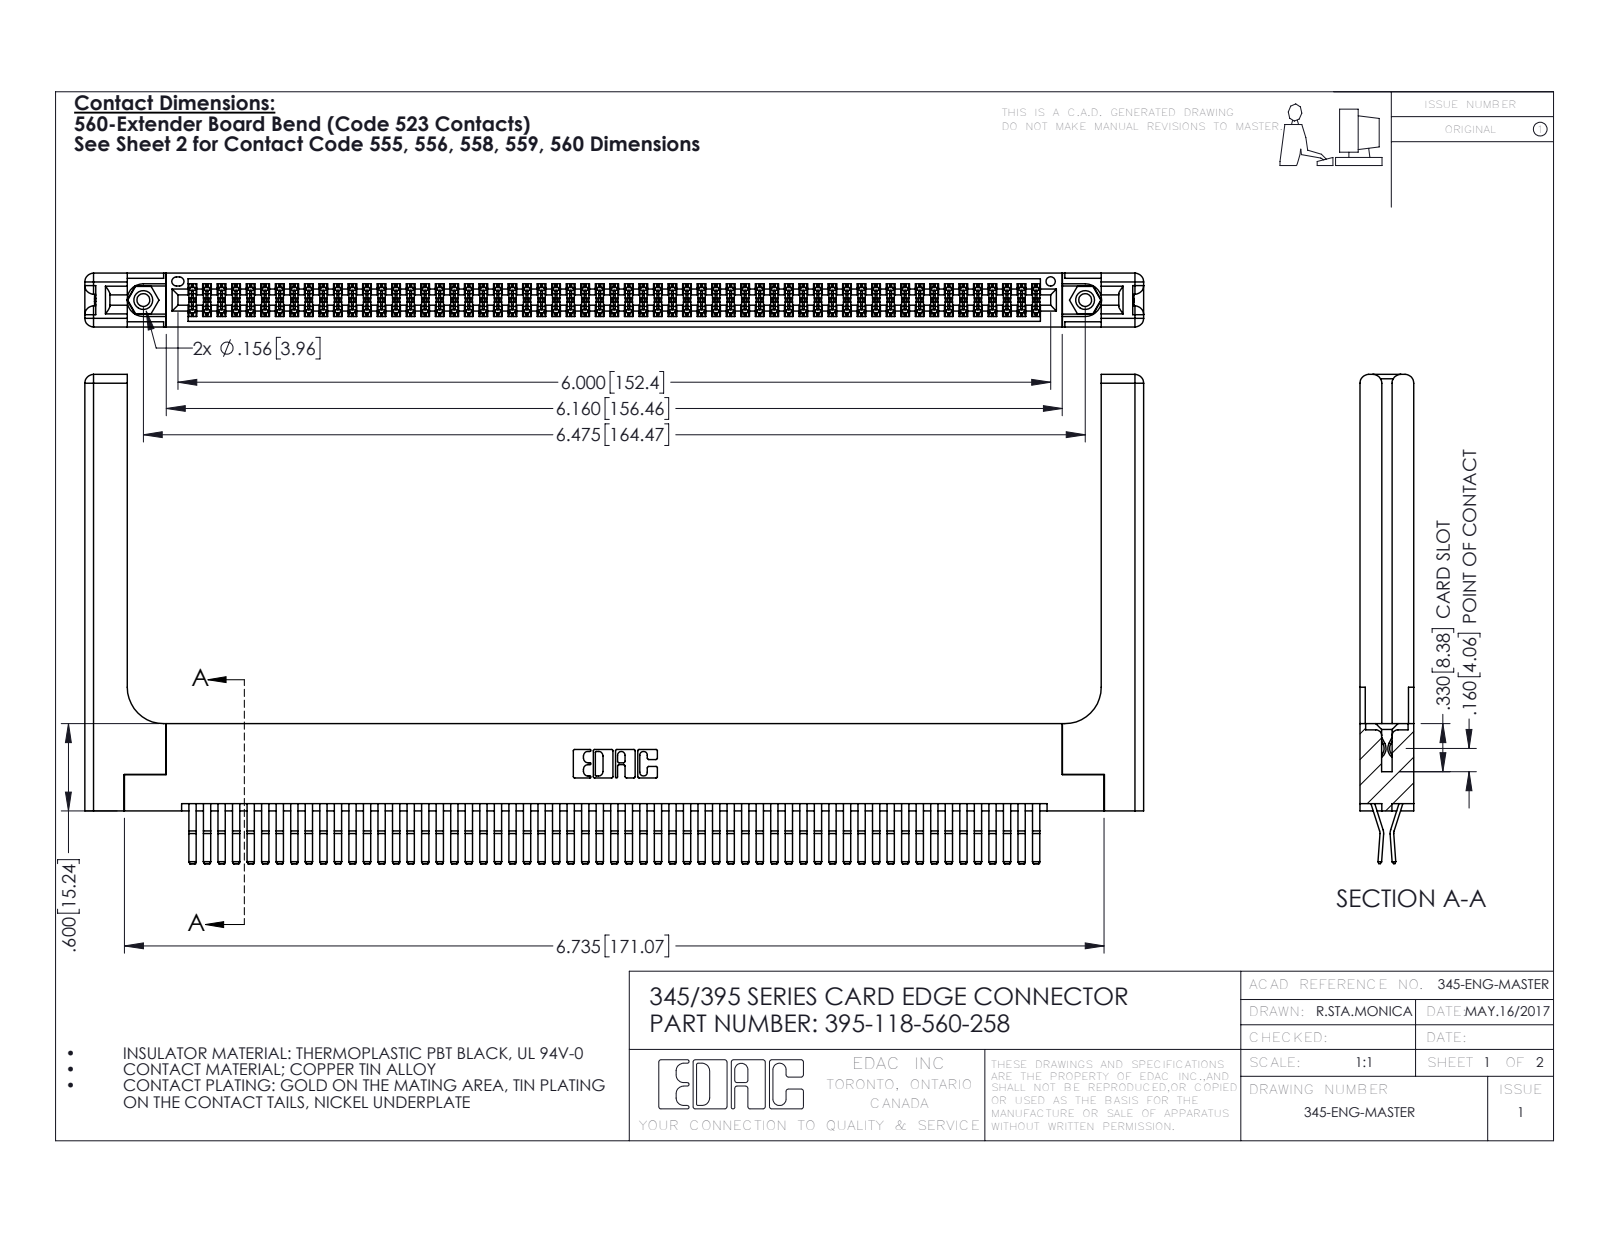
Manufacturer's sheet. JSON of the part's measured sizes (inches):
{"part_name": "395-118-560-258; 345-250-001_345-250-001-102; 345-292-001_560 Tail; 345-220-058_345-220-058 (+1 more)", "step_written_by": "SolidWorks 2016 (CONFIG_CONTROL_DESIGN)", "units": "inches", "bodies": {"solids": 123, "faces": 6518, "planar": 4122, "cylindrical": 2336, "other": 60}, "overall_size": [7.279, 3.362, 0.37], "volume_in3": 1.67, "surface_area_in2": 54.72, "round_holes": [[0.089, 2], [0.125, 2], [0.156, 2], [0.064, 1]], "round_bosses_or_shafts": [[0.155, 2]], "partial_cylinders_radius": [[0.006, 177], [0.01, 22], [0.06, 16], [0.007, 6], [0.031, 6], [0.026, 3], [0.01, 2], [0.014, 2]], "face_to_face_distances": [0.072, 0.298, 0.025, 0.37, 0.2, 0.098, 0.272, 0.225, 0.148, 0.15], "hole_center_spacings": [0.27, 6.239, 6.475]}
